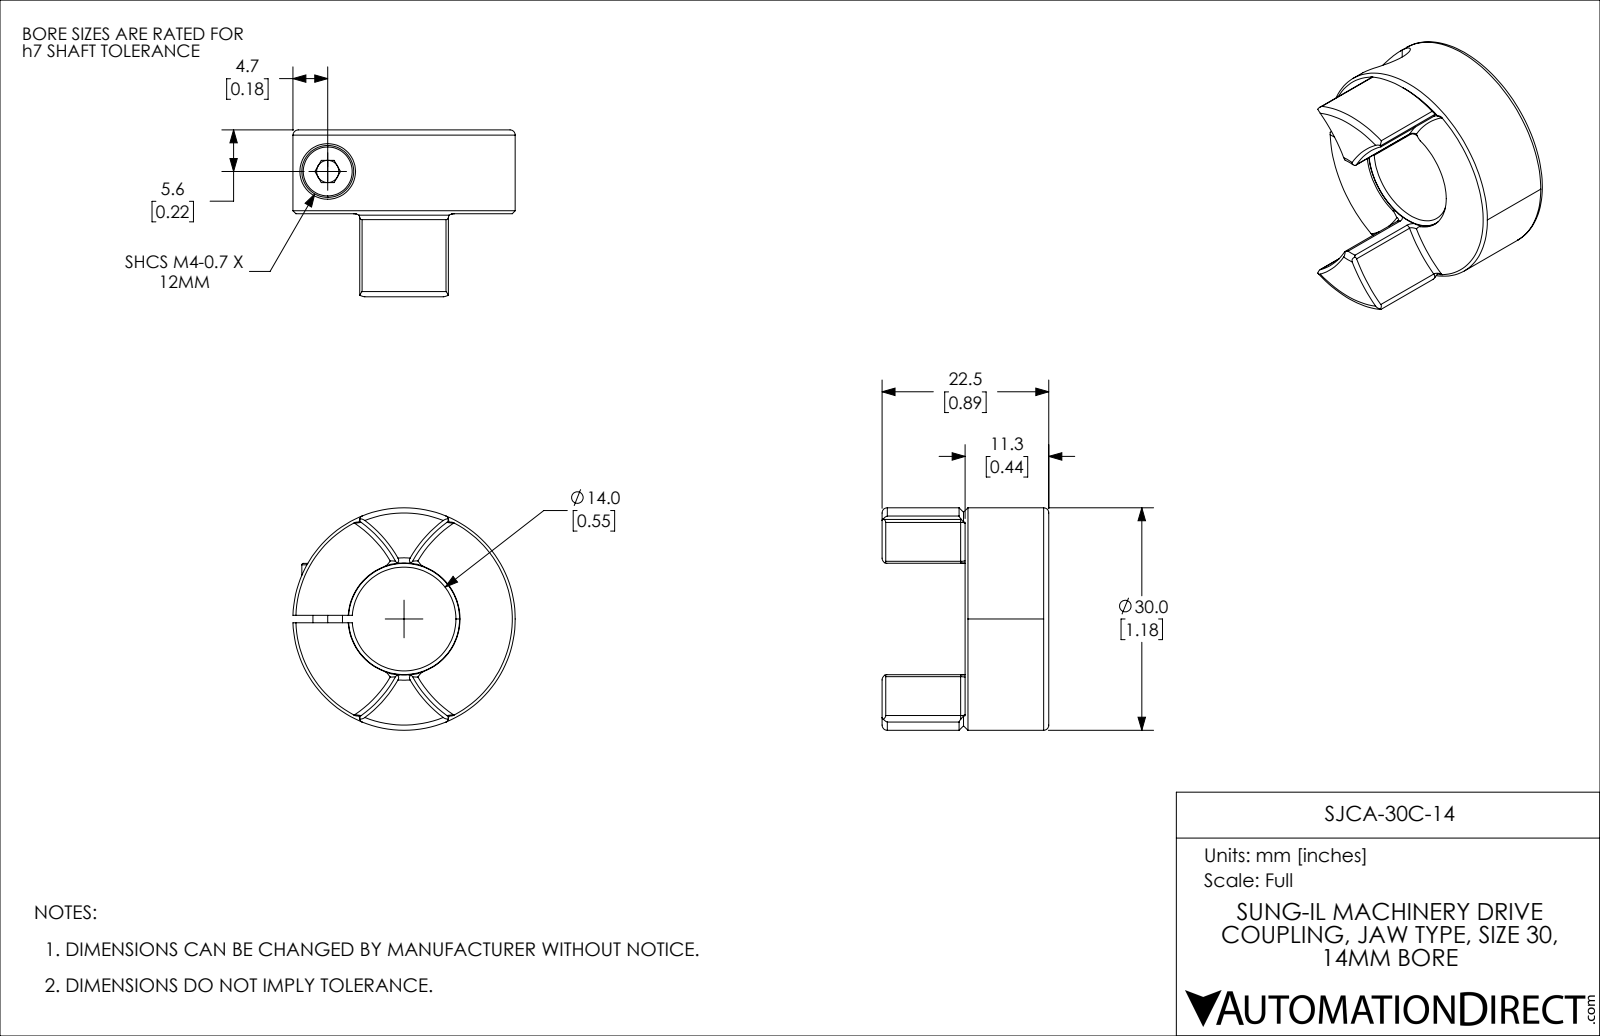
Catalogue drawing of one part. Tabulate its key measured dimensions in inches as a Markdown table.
| quantity | value |
| --- | --- |
| part name | SJCA-30C-14 |
| STEP written by | SolidWorks 2021 (CONFIG_CONTROL_DESIGN) |
| units | inches |
| bodies | 2 solids, 108 faces (27 planar, 41 cylindrical, 40 other) |
| overall size | 1.181 × 1.181 × 0.886 |
| volume | 0.434 in³ |
| surface area | 6.225 in² |
| round holes (diameter × count) | 0.118 × 1, 0.13 × 1, 0.173 × 1, 0.295 × 1, 0.551 × 1, 0.594 × 1 |
| round bosses / shafts (diameter × count) | 1.181 × 1, 0.276 × 1, 0.157 × 1 |
| partial cylindrical surfaces (radius × count) | 0.02 × 8, 0.634 × 2, 1.083 × 1 |
| main face-to-face distances | 0.445, 0.039, 0.157, 0.441, 0.886, 0.118, 0.315, 0.276, 0.354, 0.472 |
